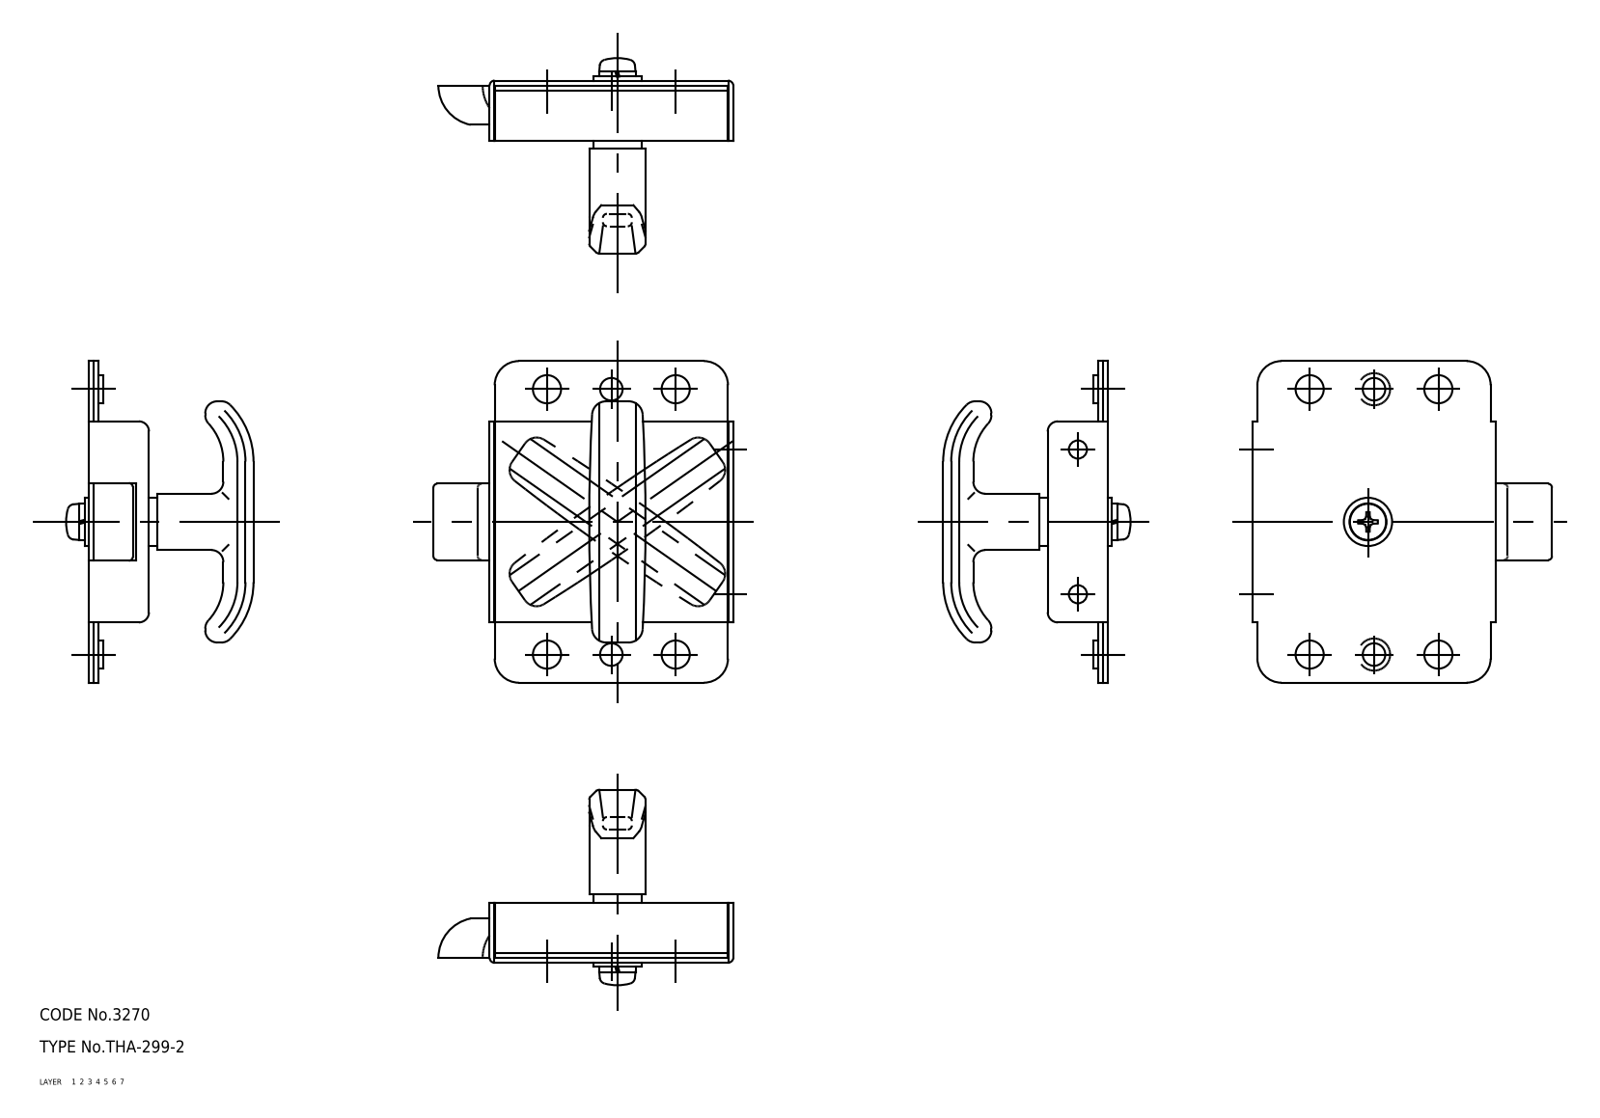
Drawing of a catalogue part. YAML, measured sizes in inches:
part_name: "latch; rivet; screw; handle (+3 more)"
step_written_by: "CADfix (AUTOMOTIVE_DESIGN)"
units: inches
bodies: {solids: 7, faces: 303, planar: 0, cylindrical: 0, other: 303}
overall_size: [3.15, 2.933, 1.833]
volume: 2.469
surface_area: 54.32
